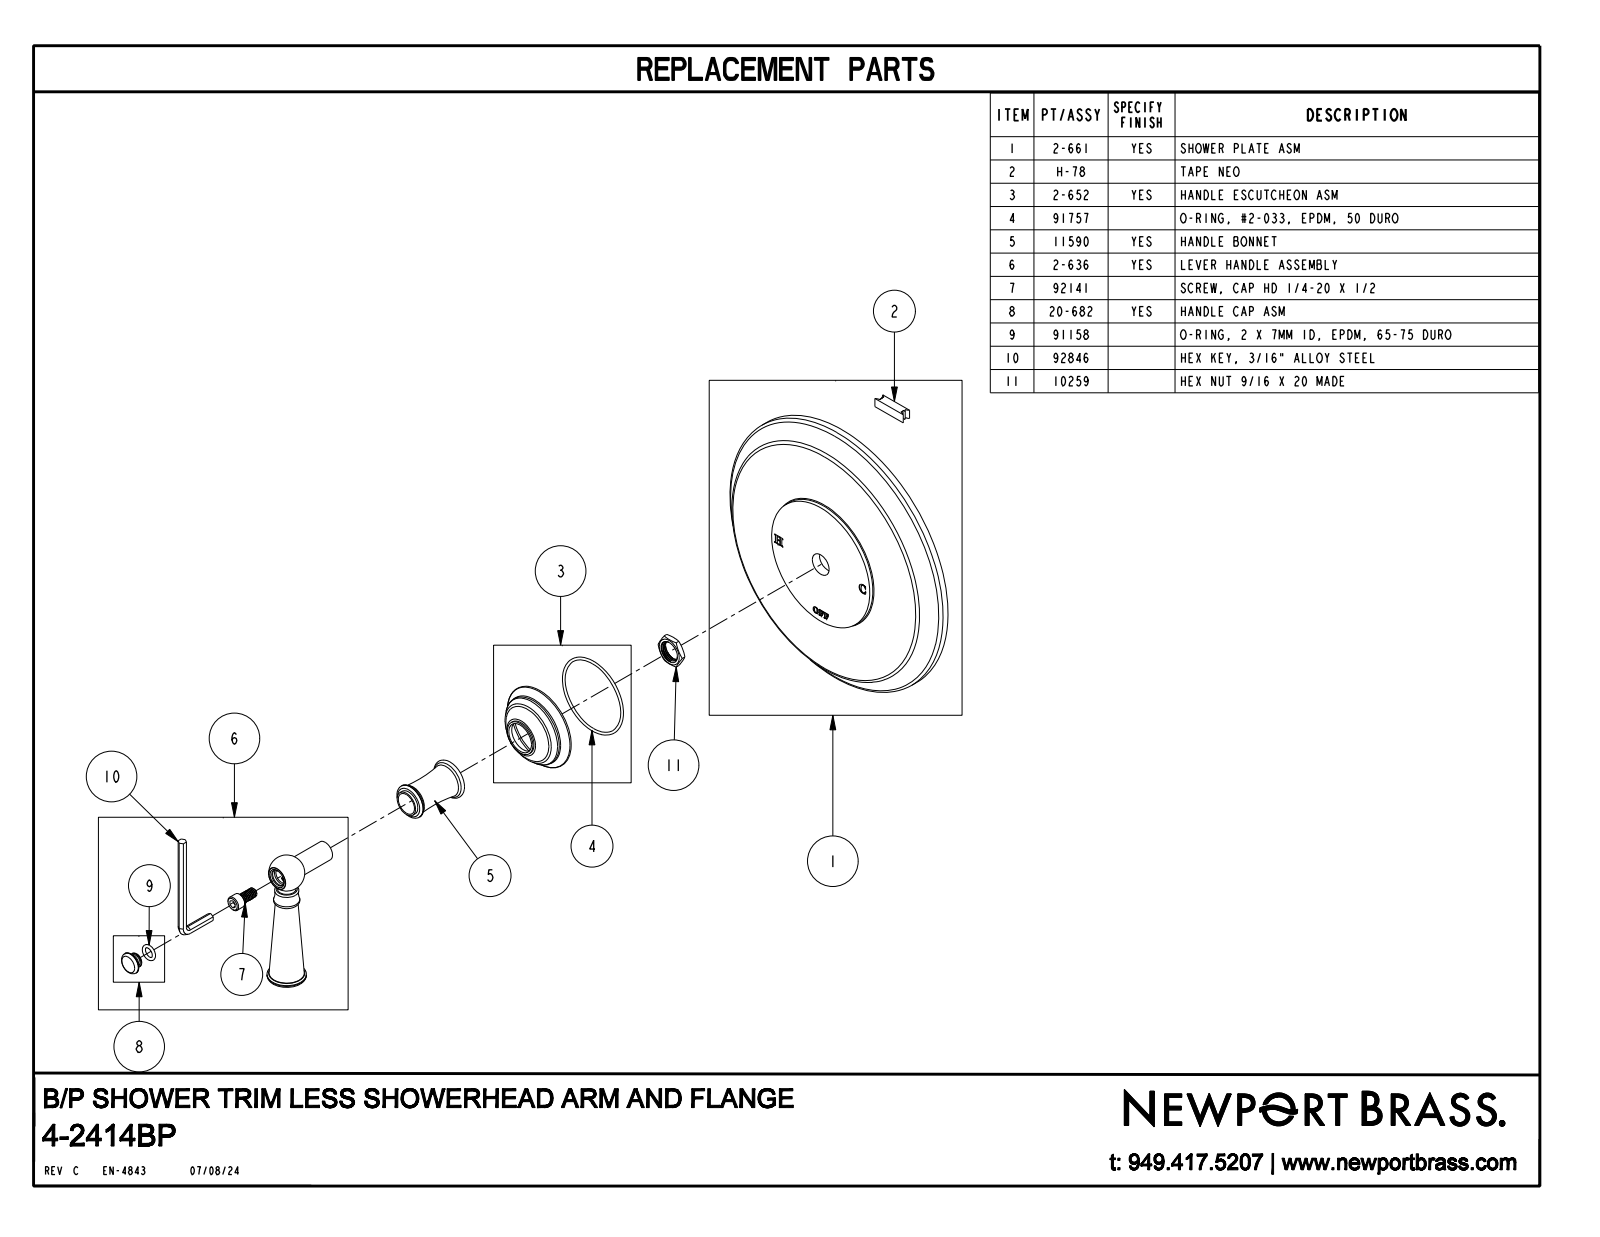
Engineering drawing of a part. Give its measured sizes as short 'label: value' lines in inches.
name: 4-2414BP
written by: CREO PARAMETRIC BY PTC INC, 2018400 (CONFIG_CONTROL_DESIGN)
unit: in
bodies: 1 solid, 210 faces (39 planar, 14 cylindrical, 157 other)
size: 7.5 × 7.5 × 4.072
volume: 29.84 in³; area: 114.4 in²
bosses: 1× ⌀7.5, 1× ⌀0.983, 1× ⌀0.9, 1× ⌀0.649, 1× ⌀0.56, 1× ⌀0.517, 1× ⌀0.461
face distances: 0.625, 0.75, 0.125, 2.89, 2.265, 2.14, 0.08, 2.97, 2.345, 2.22
